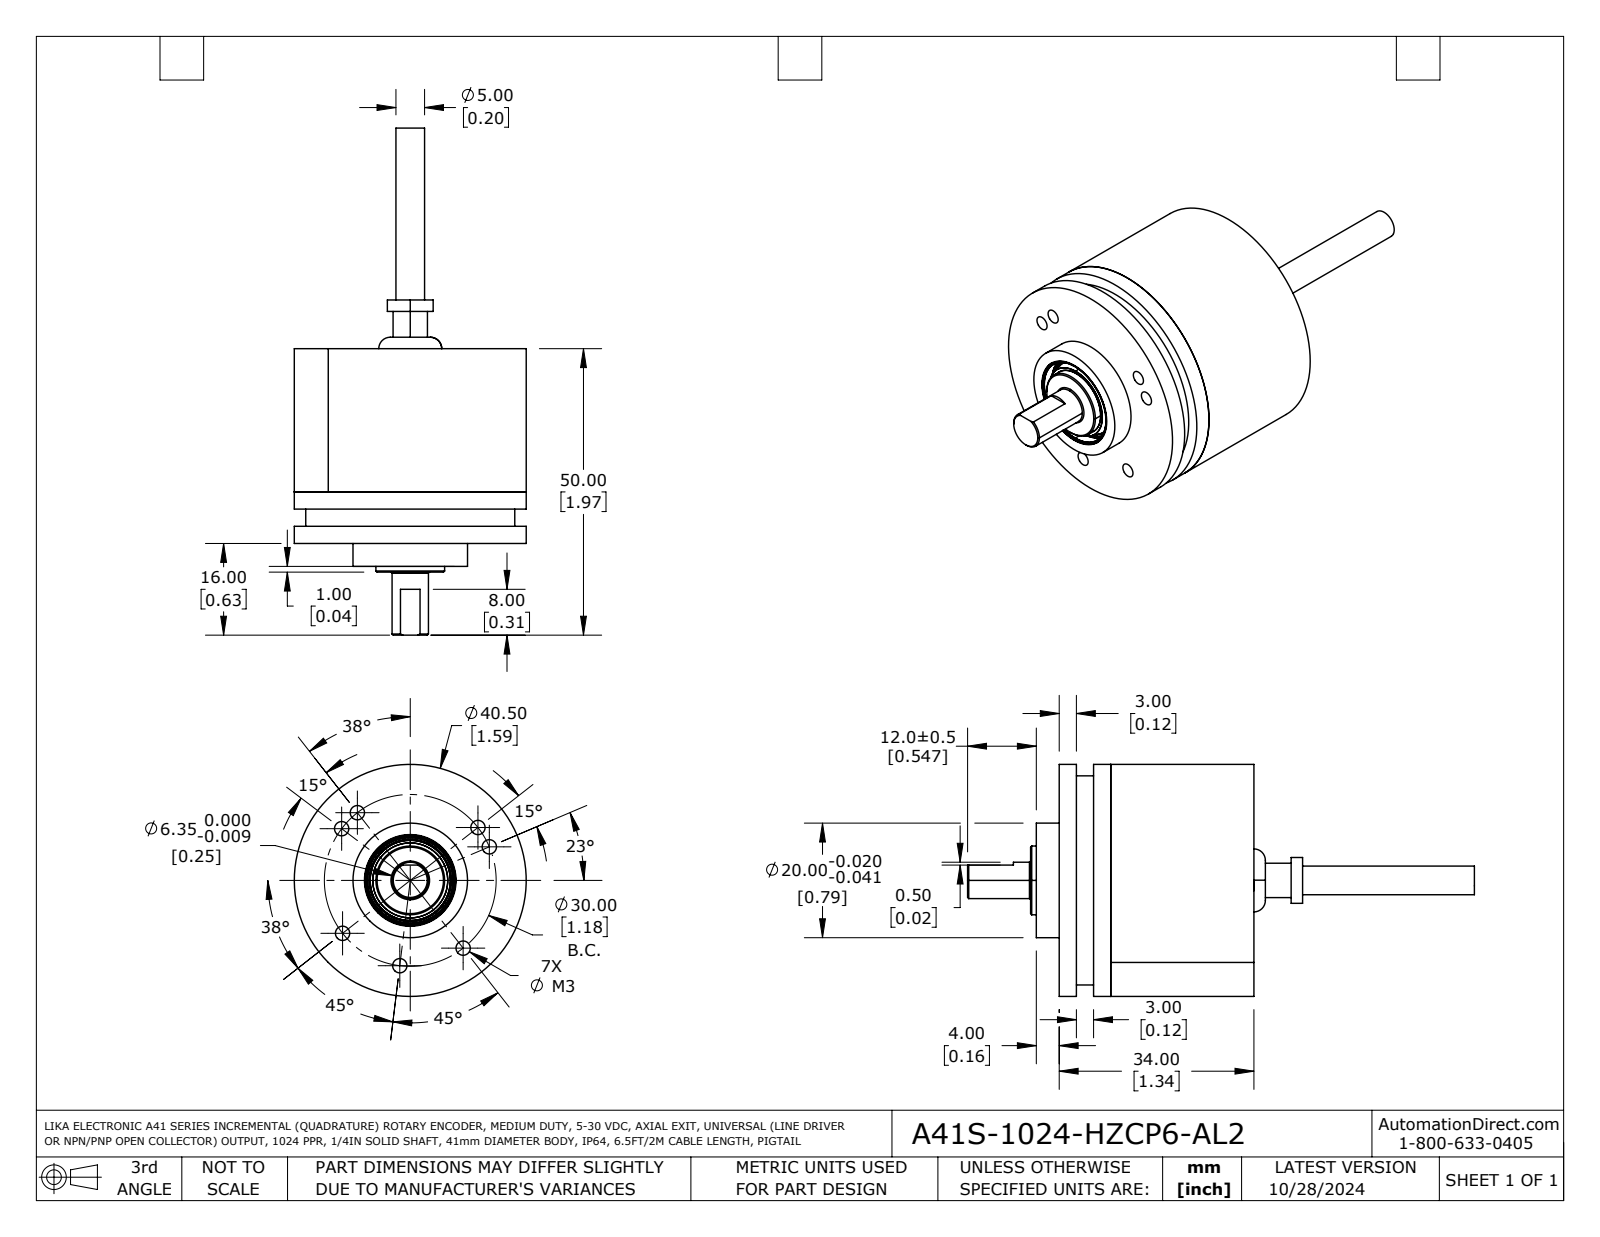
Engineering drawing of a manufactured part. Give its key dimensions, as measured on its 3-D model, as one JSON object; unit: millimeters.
{"part_name": "A41S-1024-HZCP6-AL2", "step_written_by": "SolidWorks 2021 (AUTOMOTIVE_DESIGN)", "units": "millimeters", "bodies": {"solids": 11, "faces": 422, "planar": 76, "cylindrical": 145, "other": 201}, "overall_size": [88.5, 40.5, 40.5], "volume_mm3": 19250, "surface_area_mm2": 18250, "round_holes": [[1.6, 7], [2.5, 7], [4, 3], [2.2, 2], [4.3, 1], [7.5, 1], [13, 1], [15.3, 1], [15.5, 1], [16, 1], [38.5, 1]], "round_bosses_or_shafts": [[2, 2], [40.5, 1], [38, 1], [37, 1], [36.5, 1], [20, 1], [12, 1], [8, 1]], "partial_cylinders_radius": [[1, 14], [0.2, 6], [0.2, 2]], "face_to_face_distances": [3, 34, 11, 23, 31, 2, 22, 25, 20, 1], "hole_center_spacings": [15, 17, 21.2, 2.8, 3, 21.3, 24, 31.9]}
